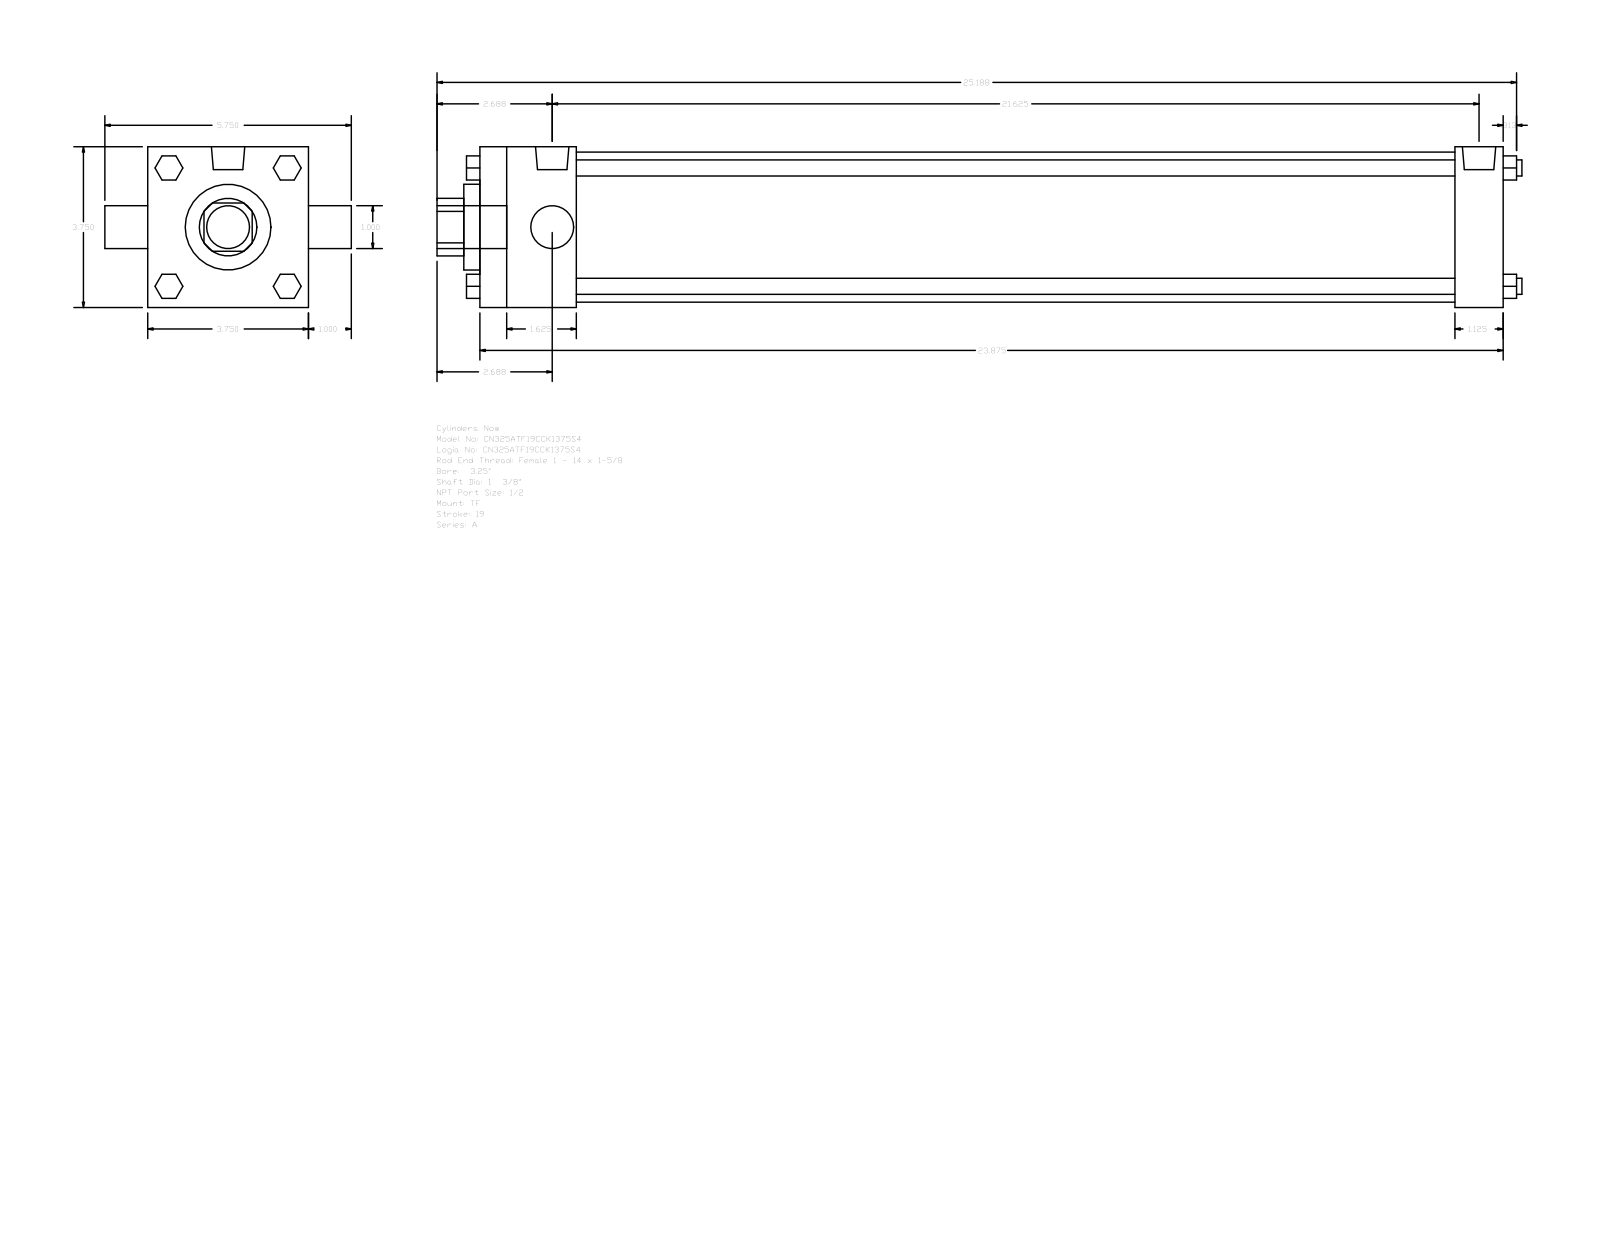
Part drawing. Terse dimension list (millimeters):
name: A_TF__0325_1.375
written by: GSSL Pune (CONFIG_CONTROL_DESIGN)
unit: mm
bodies: 0 solids, 120 faces (92 planar, 28 cylindrical, 0 other)
size: 642.94 × 146.05 × 95.25
holes: 1× ⌀25.4, 1× ⌀34.92, 1× ⌀50.8, 1× ⌀88.9
bosses: 4× ⌀9.53, 3× ⌀8.73, 2× ⌀19.77, 1× ⌀25.4
rounds: 1× R17.06
face distances: 95.24, 606.43, 28.58, 57.15, 577.85, 520.7, 549.28, 9.52, 66.67, 587.37
